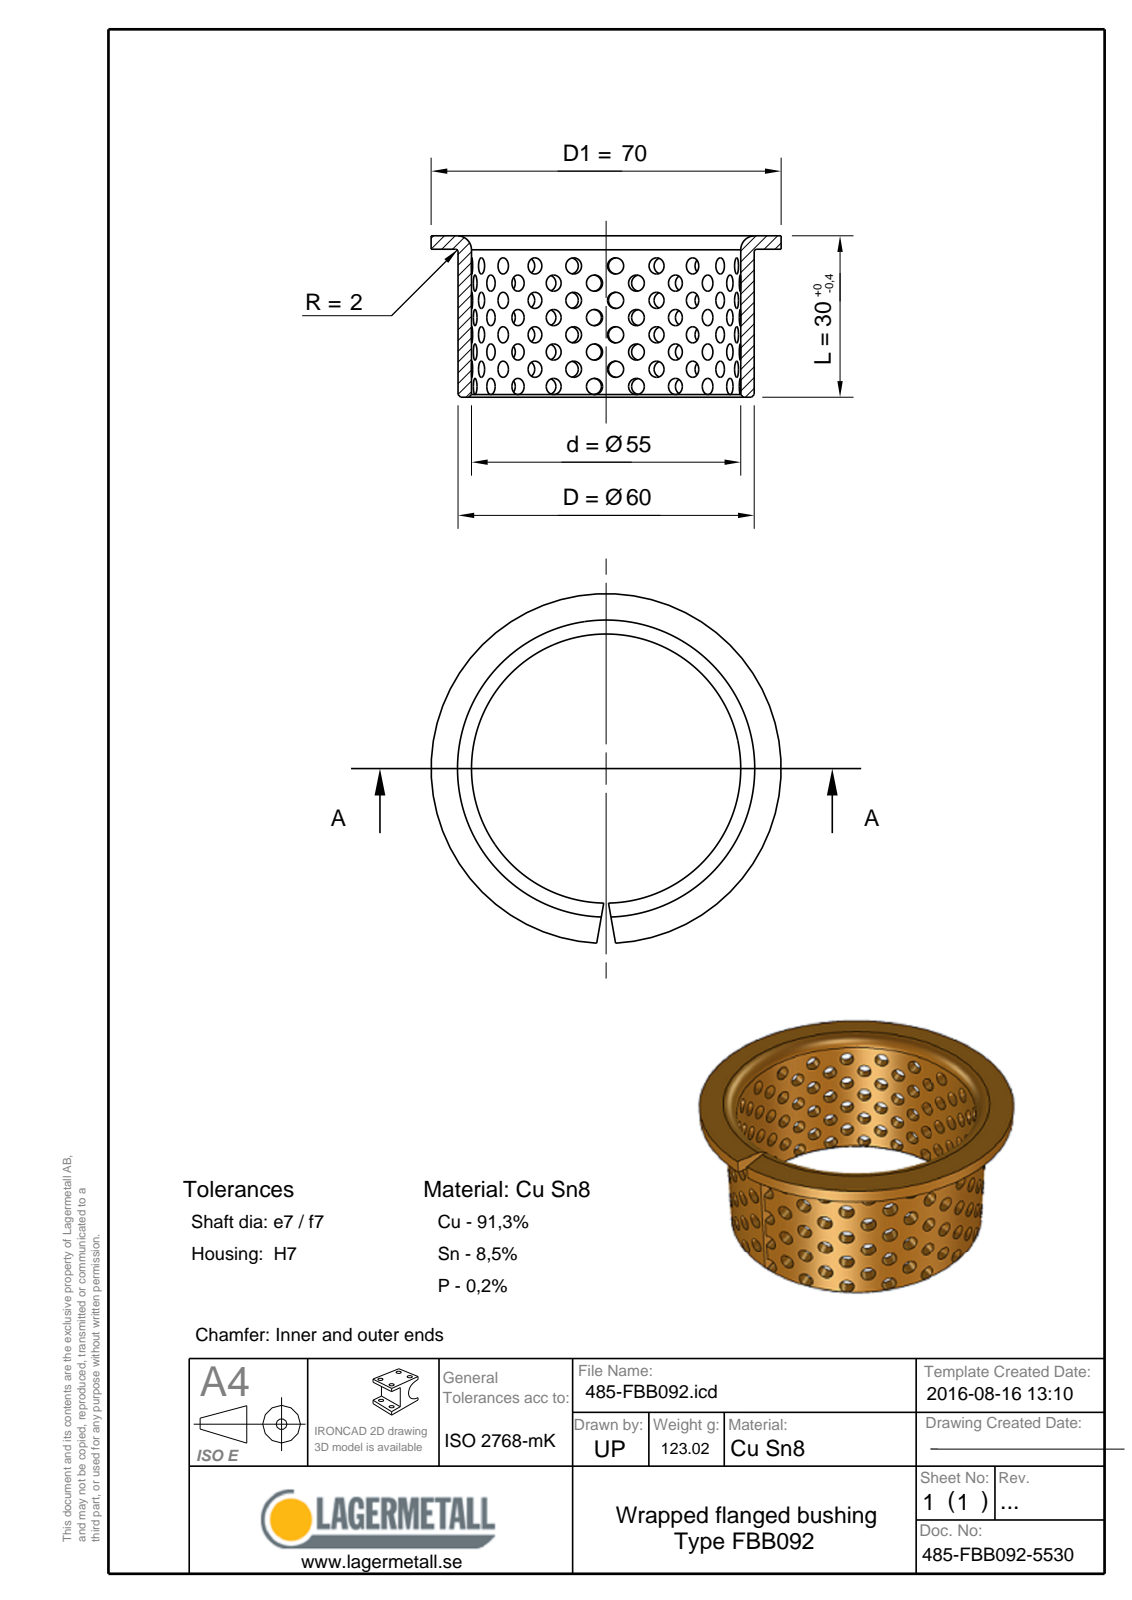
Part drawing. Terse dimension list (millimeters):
name: 485-FBB092-5530
written by: Spatial InterOp 3D (CONFIG_CONTROL_DESIGN)
unit: mm
bodies: 1 solid, 12 faces (5 planar, 3 cylindrical, 4 other)
size: 70 × 69.96 × 30
volume: 15 187 mm³; area: 13 247 mm²
holes: 1× ⌀55
bosses: 1× ⌀70, 1× ⌀60
face distances: 2.5, 27.5, 30
